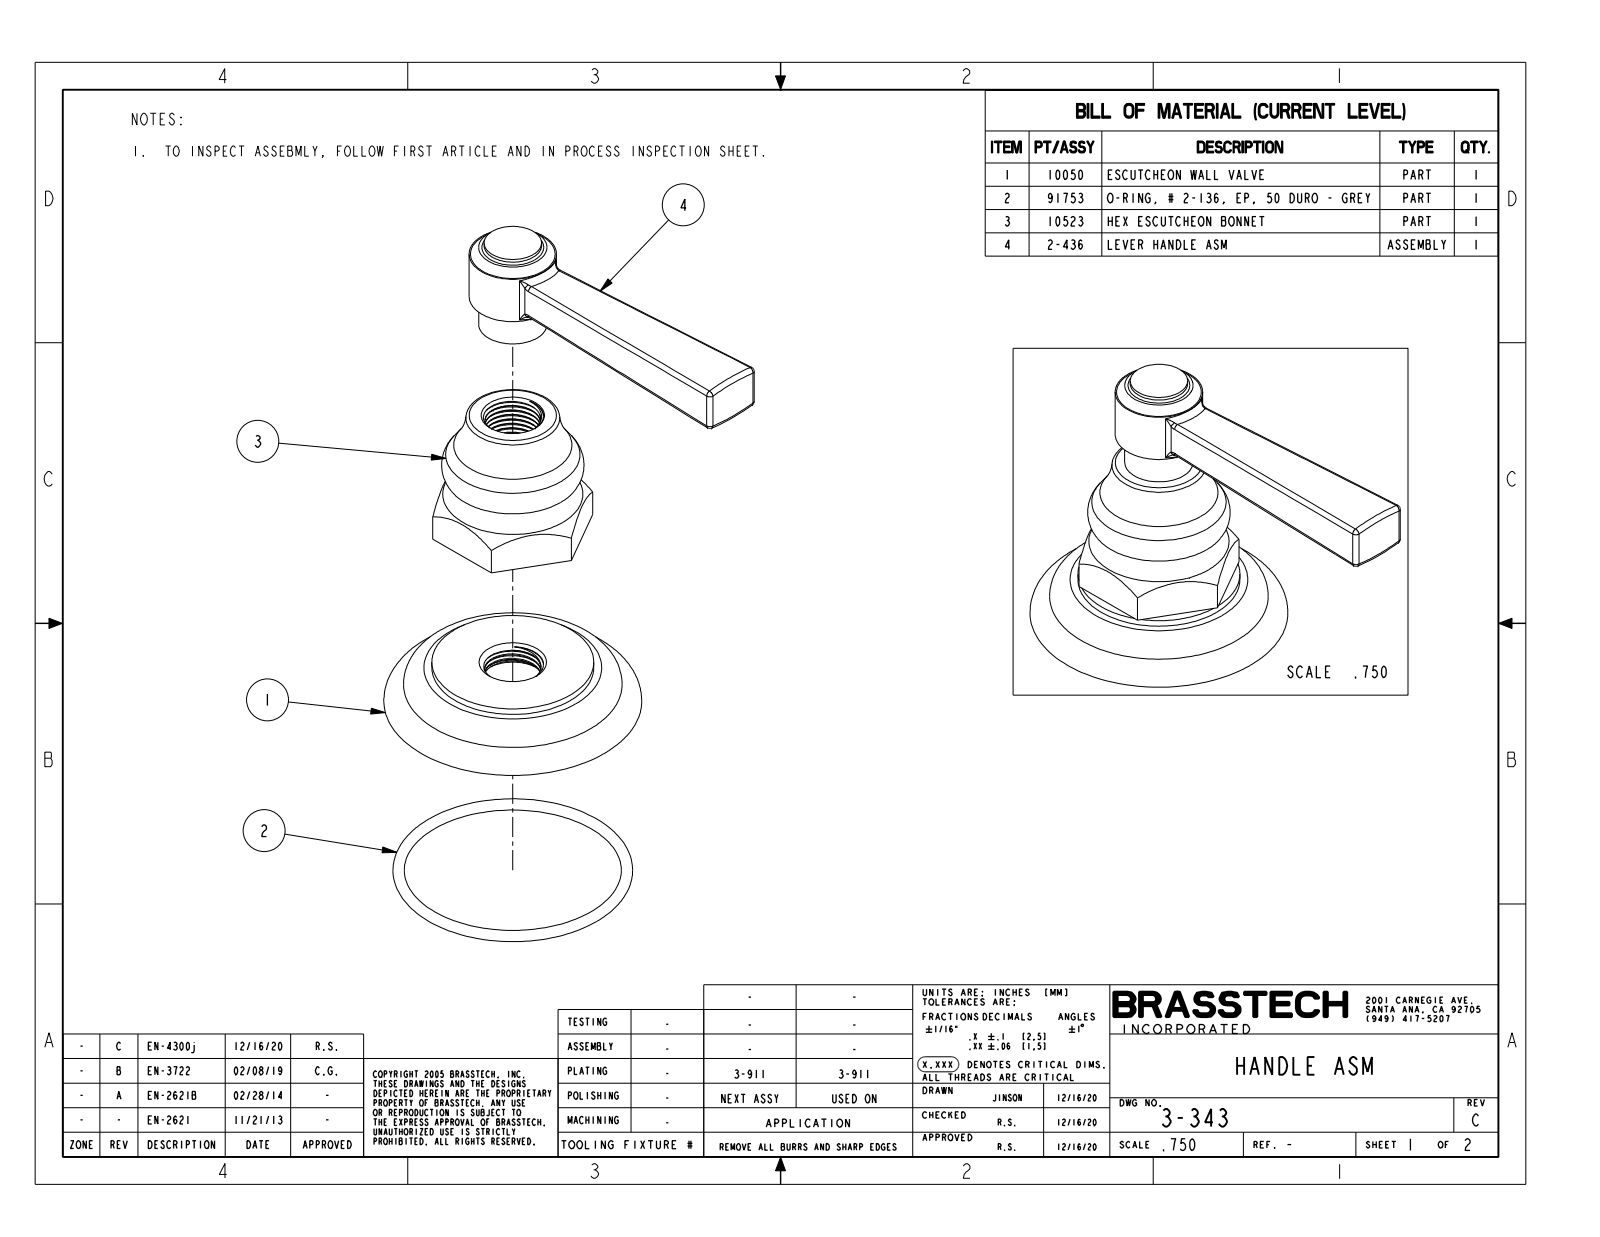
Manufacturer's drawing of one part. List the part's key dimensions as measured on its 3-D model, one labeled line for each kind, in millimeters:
Part name (STEP PRODUCT): 3-343
STEP written by: CREO PARAMETRIC BY PTC INC, 2018400 (CONFIG_CONTROL_DESIGN)
Units: millimetres
Bodies: 1 solid, 91 faces (29 planar, 14 cylindrical, 48 other)
Overall size (bounding box): 102.4 × 66.2 × 59.9
Volume: 60 810 mm³ · Surface area: 13 990 mm²
Round bosses / shafts (diameter × count): ⌀37.6 ×1, ⌀20.3 ×1, ⌀15.9 ×1, ⌀13.3 ×1, ⌀10.2 ×1
Partial cylindrical surfaces — rounded edges, fillets, slot ends (radius × count): R1 ×2, R1.4 ×2
Main face-to-face distances: 33.4, 42.8, 9.5, 33.3, 33.4, 11.1, 1.6, 31.8, 66.2, 56.6
